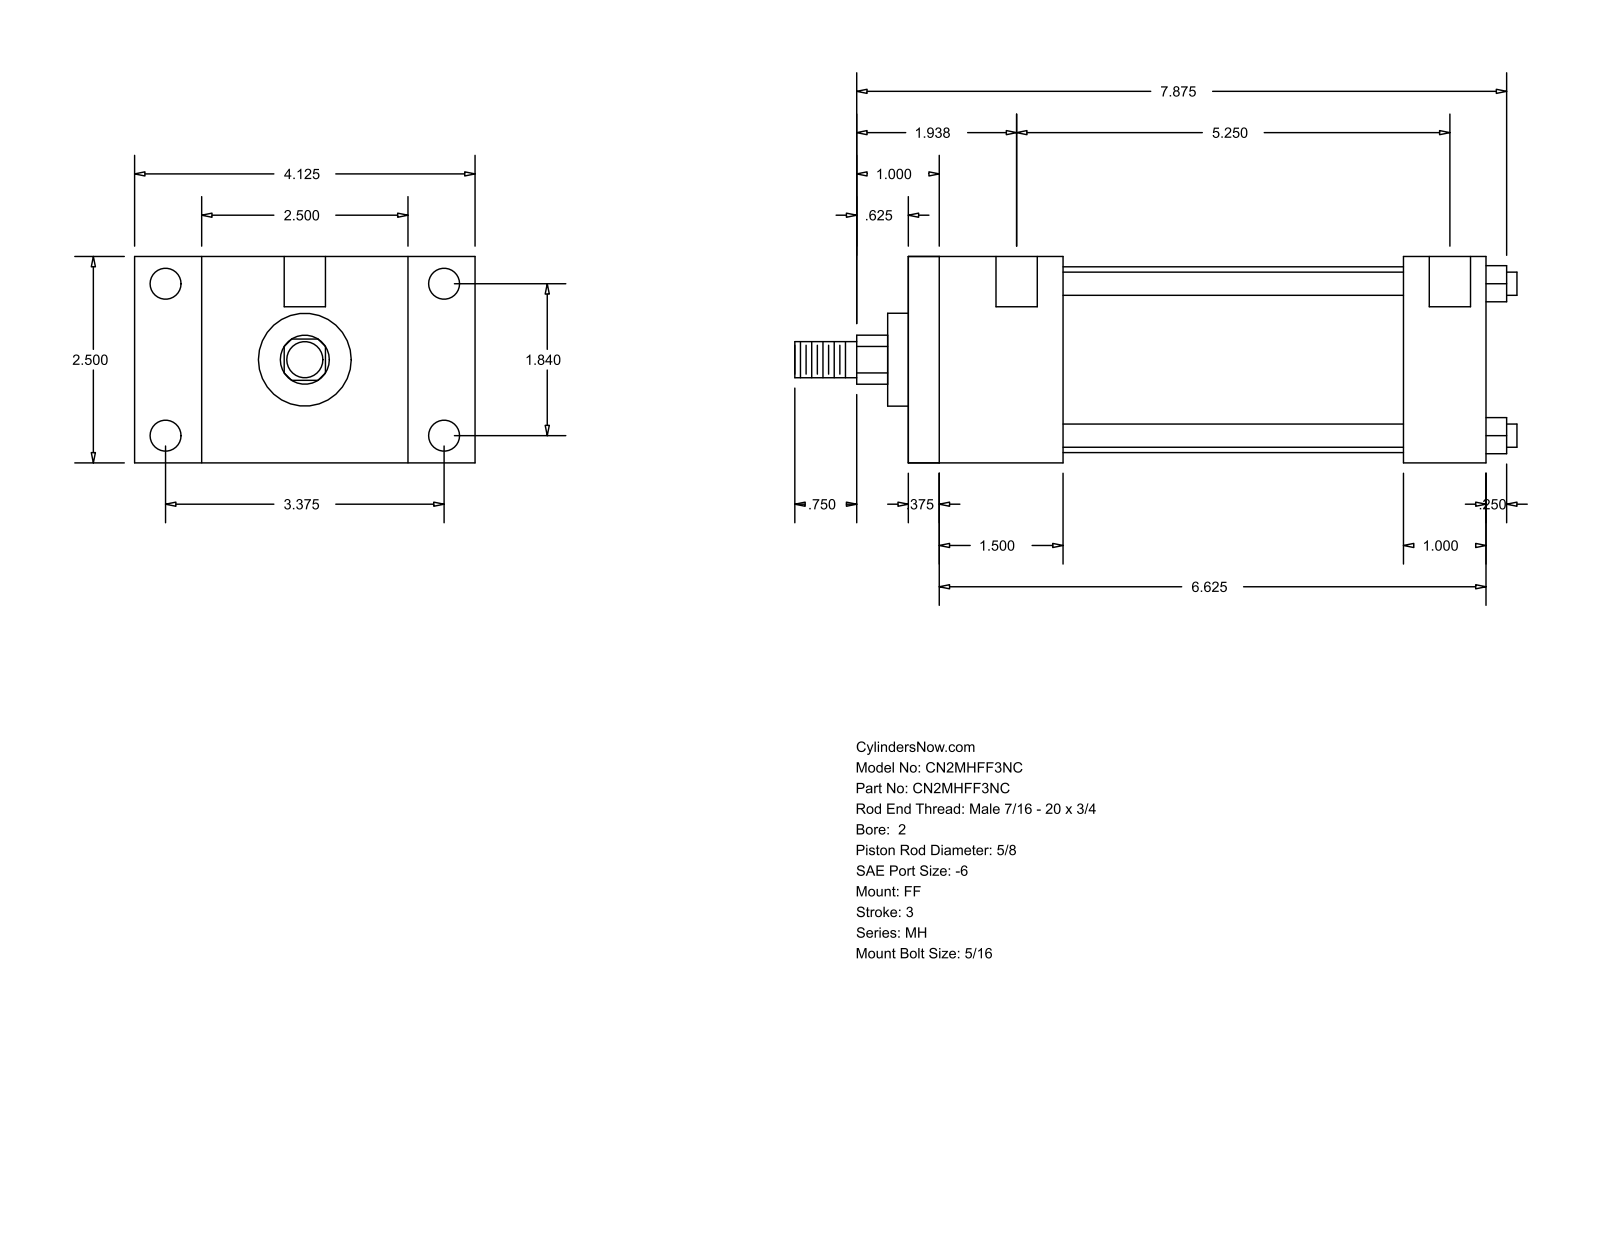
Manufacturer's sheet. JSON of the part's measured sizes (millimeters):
{"part_name": "MH_FF__0200_0.625", "step_written_by": "GSSL Pune (CONFIG_CONTROL_DESIGN)", "units": "millimeters", "bodies": {"solids": 0, "faces": 92, "planar": 64, "cylindrical": 28, "other": 0}, "overall_size": [222.25, 104.78, 63.5], "round_holes": [[5.56, 4], [9.53, 4], [12.7, 2]], "round_bosses_or_shafts": [[7.14, 4], [57.15, 1], [28.57, 1], [15.88, 1], [11.11, 1]], "partial_cylinders_radius": [[7.54, 1]], "face_to_face_distances": [63.5, 177.8, 9.52, 168.28, 104.78, 25.4, 38.1, 47.62, 152.4, 142.88], "hole_center_spacings": [46.74, 85.72, 97.63, 141.29, 3.18, 4.76, 133.35, 136.53]}
